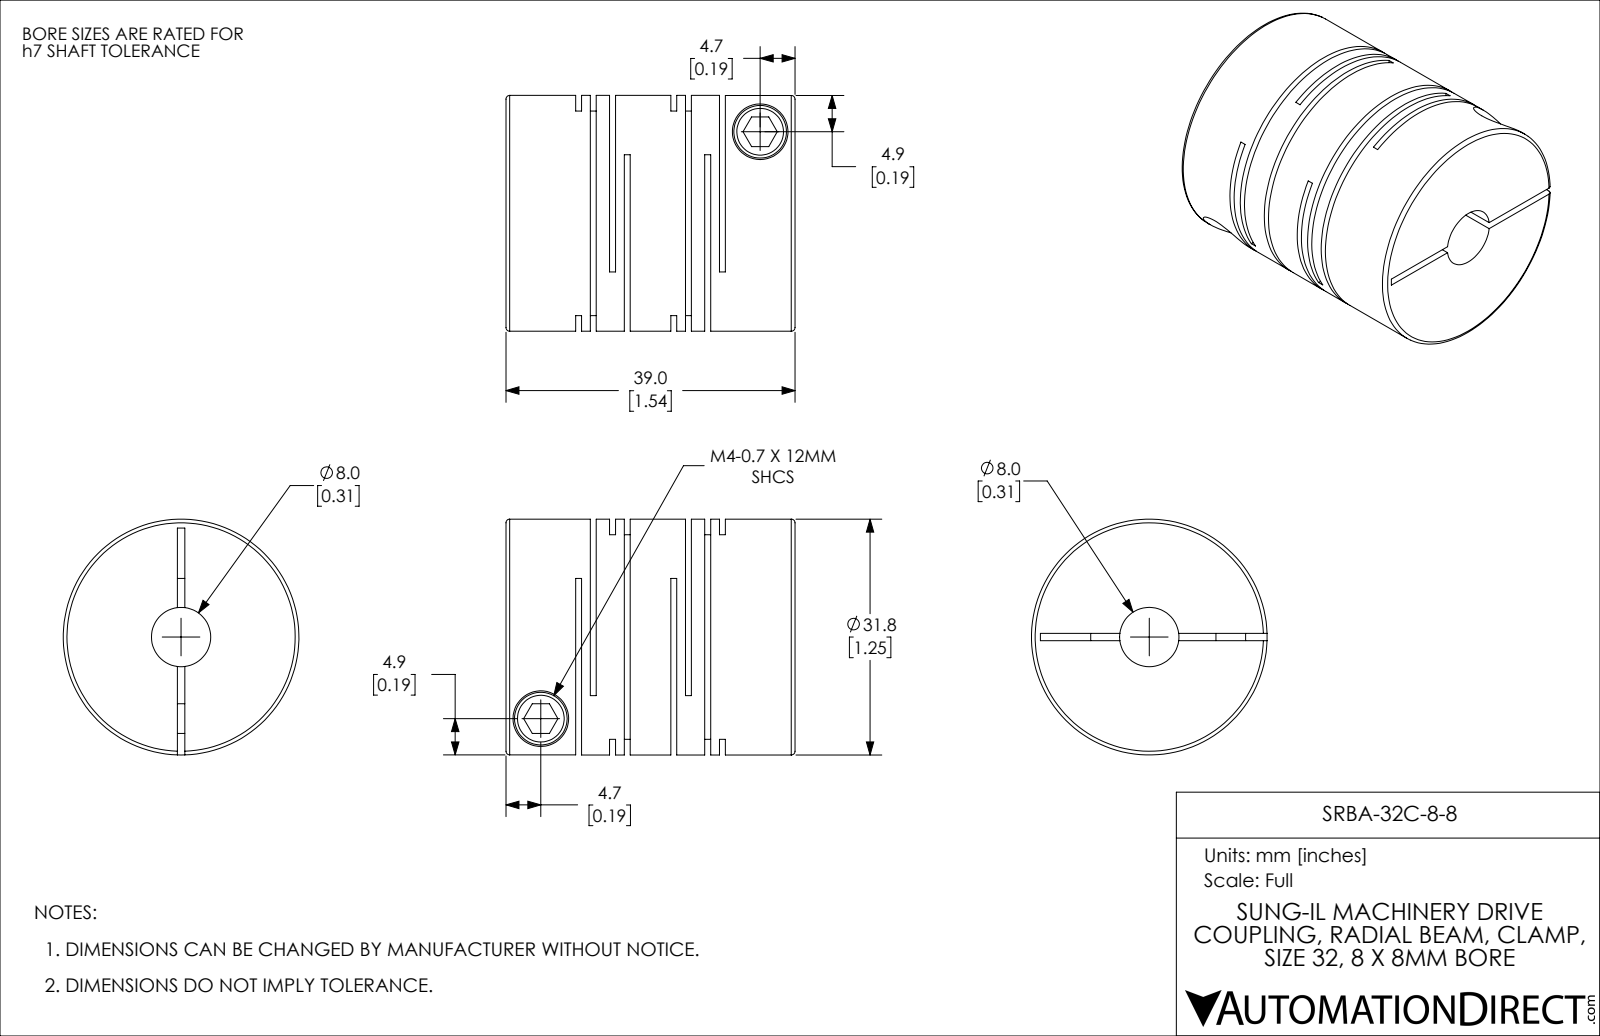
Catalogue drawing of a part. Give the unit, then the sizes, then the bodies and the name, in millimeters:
Units: millimetres
Overall size (bounding box): 39 × 31.8 × 31.8
Round holes (diameter × count): ⌀4 ×2, ⌀7.5 ×2, ⌀8 ×1
Round bosses / shafts (diameter × count): ⌀7.1 ×2, ⌀31.8 ×1
Main face-to-face distances: 0.8, 1.98, 12.84, 4.58, 12.04, 1.18, 10.86, 3.78, 8.26, 2.6
Volume: 24 334 mm³ · Surface area: 16 580 mm²
Bodies: 1 solid, 114 faces (60 planar, 42 cylindrical, 12 other)
Part name (STEP PRODUCT): SRBA-32C-8-8
STEP written by: SolidWorks 2021 (CONFIG_CONTROL_DESIGN)
